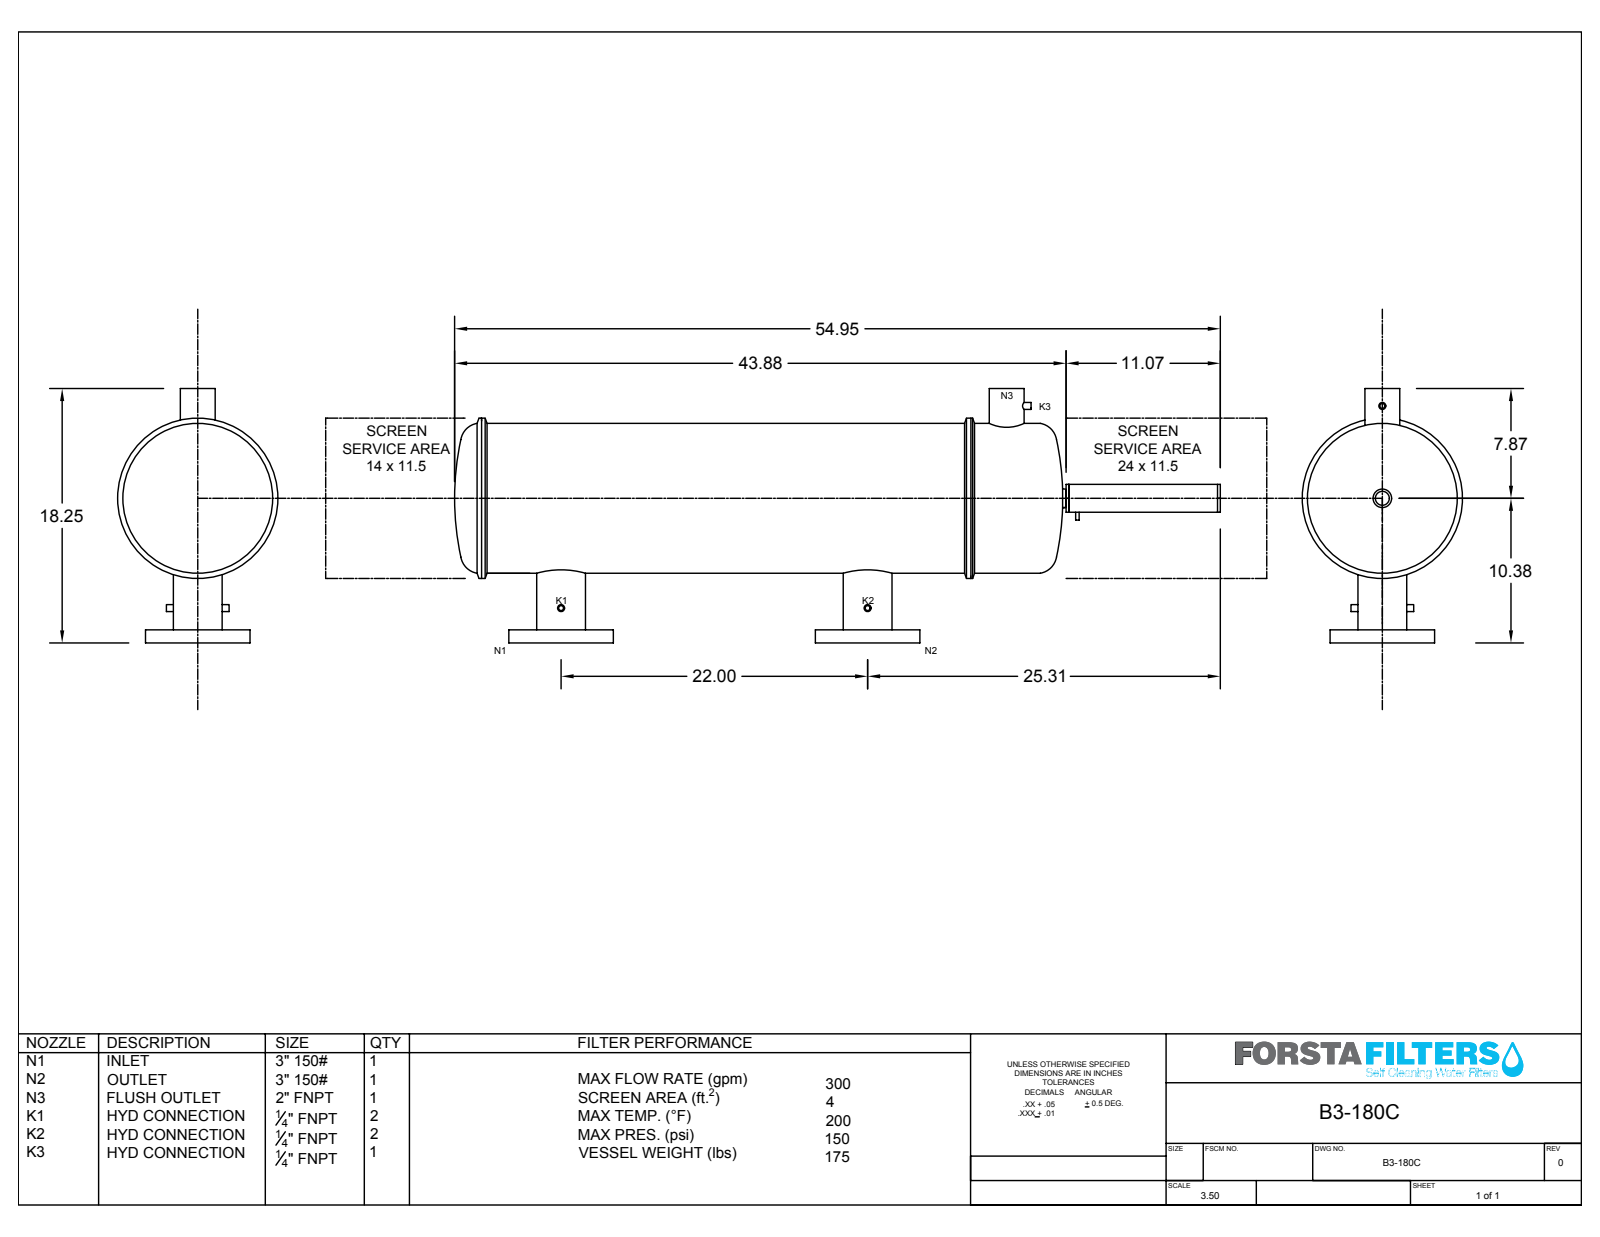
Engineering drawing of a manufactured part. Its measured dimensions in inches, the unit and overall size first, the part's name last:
Units: inches
Overall size (bounding box): 61.622 × 18.25 × 11.5
Round holes (diameter × count): ⌀0.75 ×8, ⌀0.25 ×3, ⌀1 ×2, ⌀3 ×2, ⌀0.093 ×1, ⌀0.936 ×1, ⌀2 ×1, ⌀10.356 ×1
Round bosses / shafts (diameter × count): ⌀0.644 ×3, ⌀7.5 ×2, ⌀3.394 ×2, ⌀11.5 ×1, ⌀10.75 ×1, ⌀2.394 ×1, ⌀2 ×1, ⌀1.33 ×1
Partial cylindrical surfaces — rounded edges, fillets, slot ends (radius × count): R1 ×2
Main face-to-face distances: 0.94, 0.25, 0.2, 14.042, 59.485, 45.643, 13.842, 45.443, 59.685, 14.242
Hole centre spacings: 4.272, 24.4, 2.67, 3, 3.372, 4.243, 6.041, 10.867
Volume: 464.7 in³ · Surface area: 4 019 in²
Bodies: 6 solids, 160 faces (40 planar, 84 cylindrical, 36 other)
Part name (STEP PRODUCT): B3-180C
STEP written by: SolidWorks 2017 (CONFIG_CONTROL_DESIGN)
